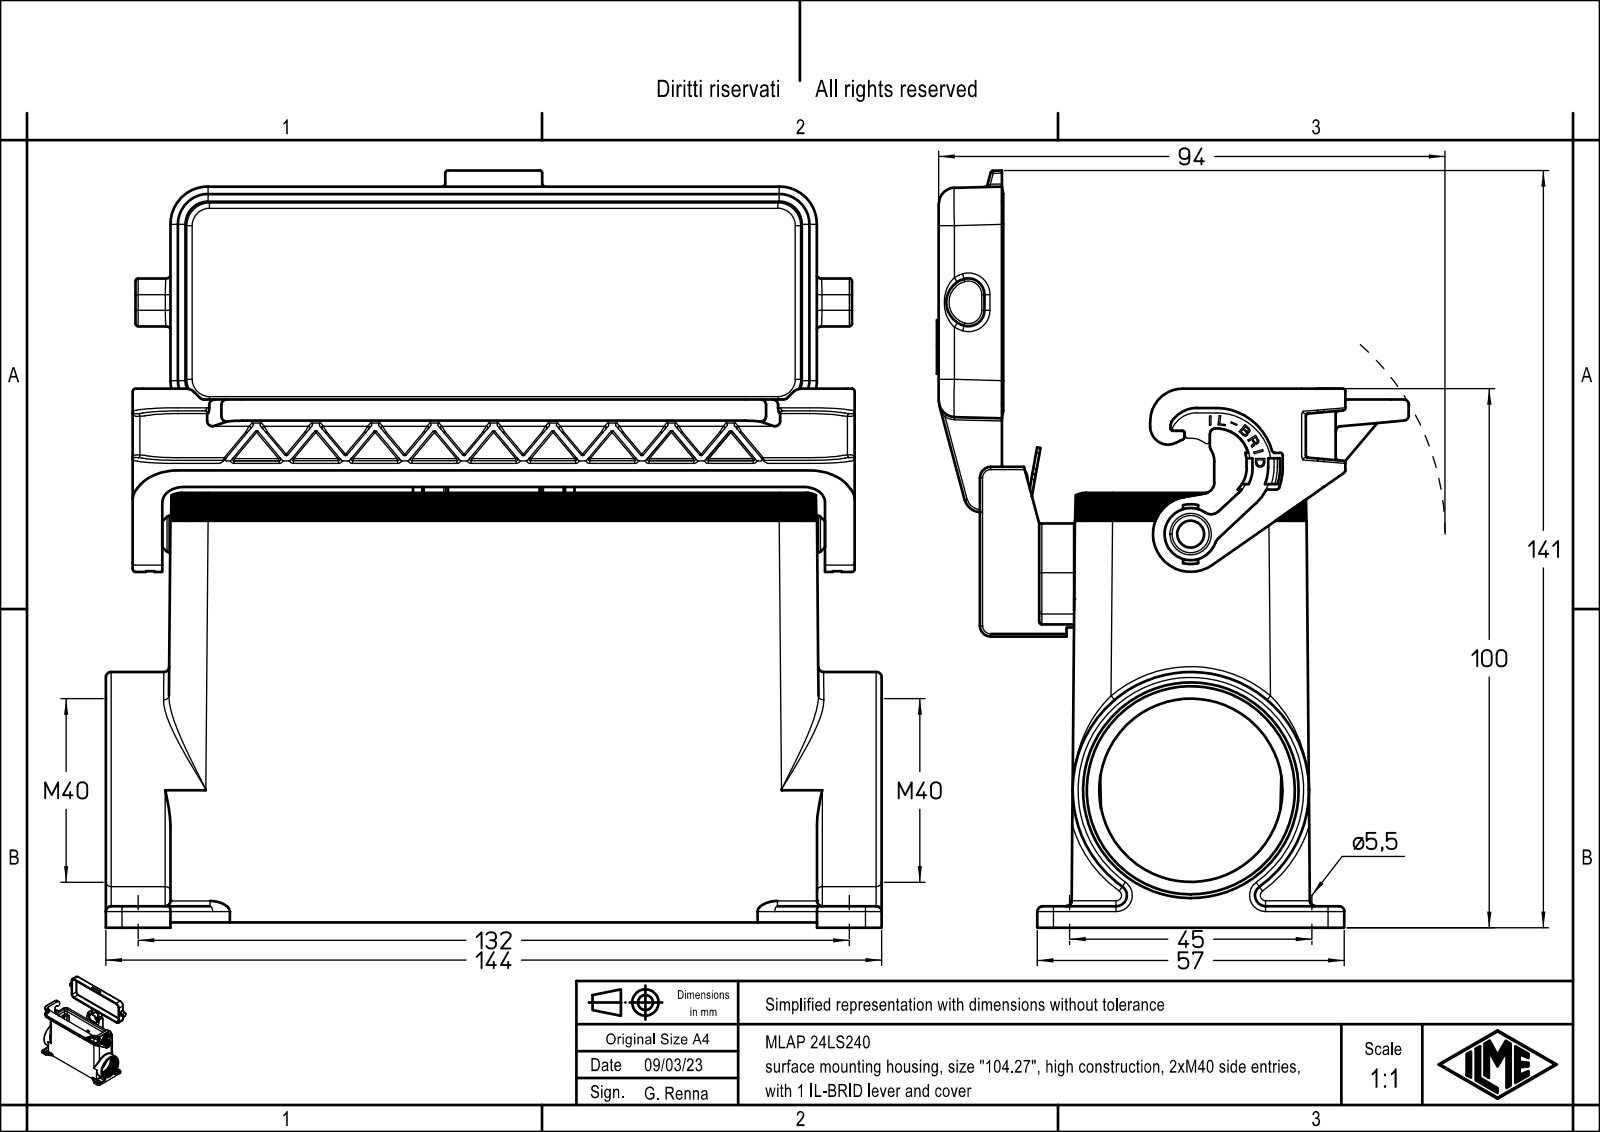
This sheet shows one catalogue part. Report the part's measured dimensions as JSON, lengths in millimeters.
{"part_name": "MLAP 24LS240", "step_written_by": "Creo Elements/Direct Modeling 20.1B 02-Apr-2019 (C) Parametric Technology GmbH (AUTOMOTIVE_DESIGN)", "units": "millimeters", "bodies": {"solids": 1, "faces": 1454, "planar": 839, "cylindrical": 408, "other": 207}, "overall_size": [144, 140.49, 87.76], "volume_mm3": 180309, "surface_area_mm2": 104877, "round_holes": [[3, 4], [3.5, 4], [5.5, 4], [3.25, 1], [5.4, 1], [7.7, 1], [34, 1], [38.6, 1]], "round_bosses_or_shafts": [[43.87, 1], [8.4, 1], [6.9, 1], [6.8, 1], [5.2, 1], [3.2, 1]], "partial_cylinders_radius": [[0.5, 29], [0.1, 27], [1, 24], [0.2, 23], [3, 23], [0.17, 17], [0.33, 16], [2, 15]], "face_to_face_distances": [2, 3, 2.8, 69.71, 71.71, 7, 4, 97, 94, 1], "hole_center_spacings": [16.64, 38.63, 118.34, 123.37, 27, 45, 104, 107.45]}
